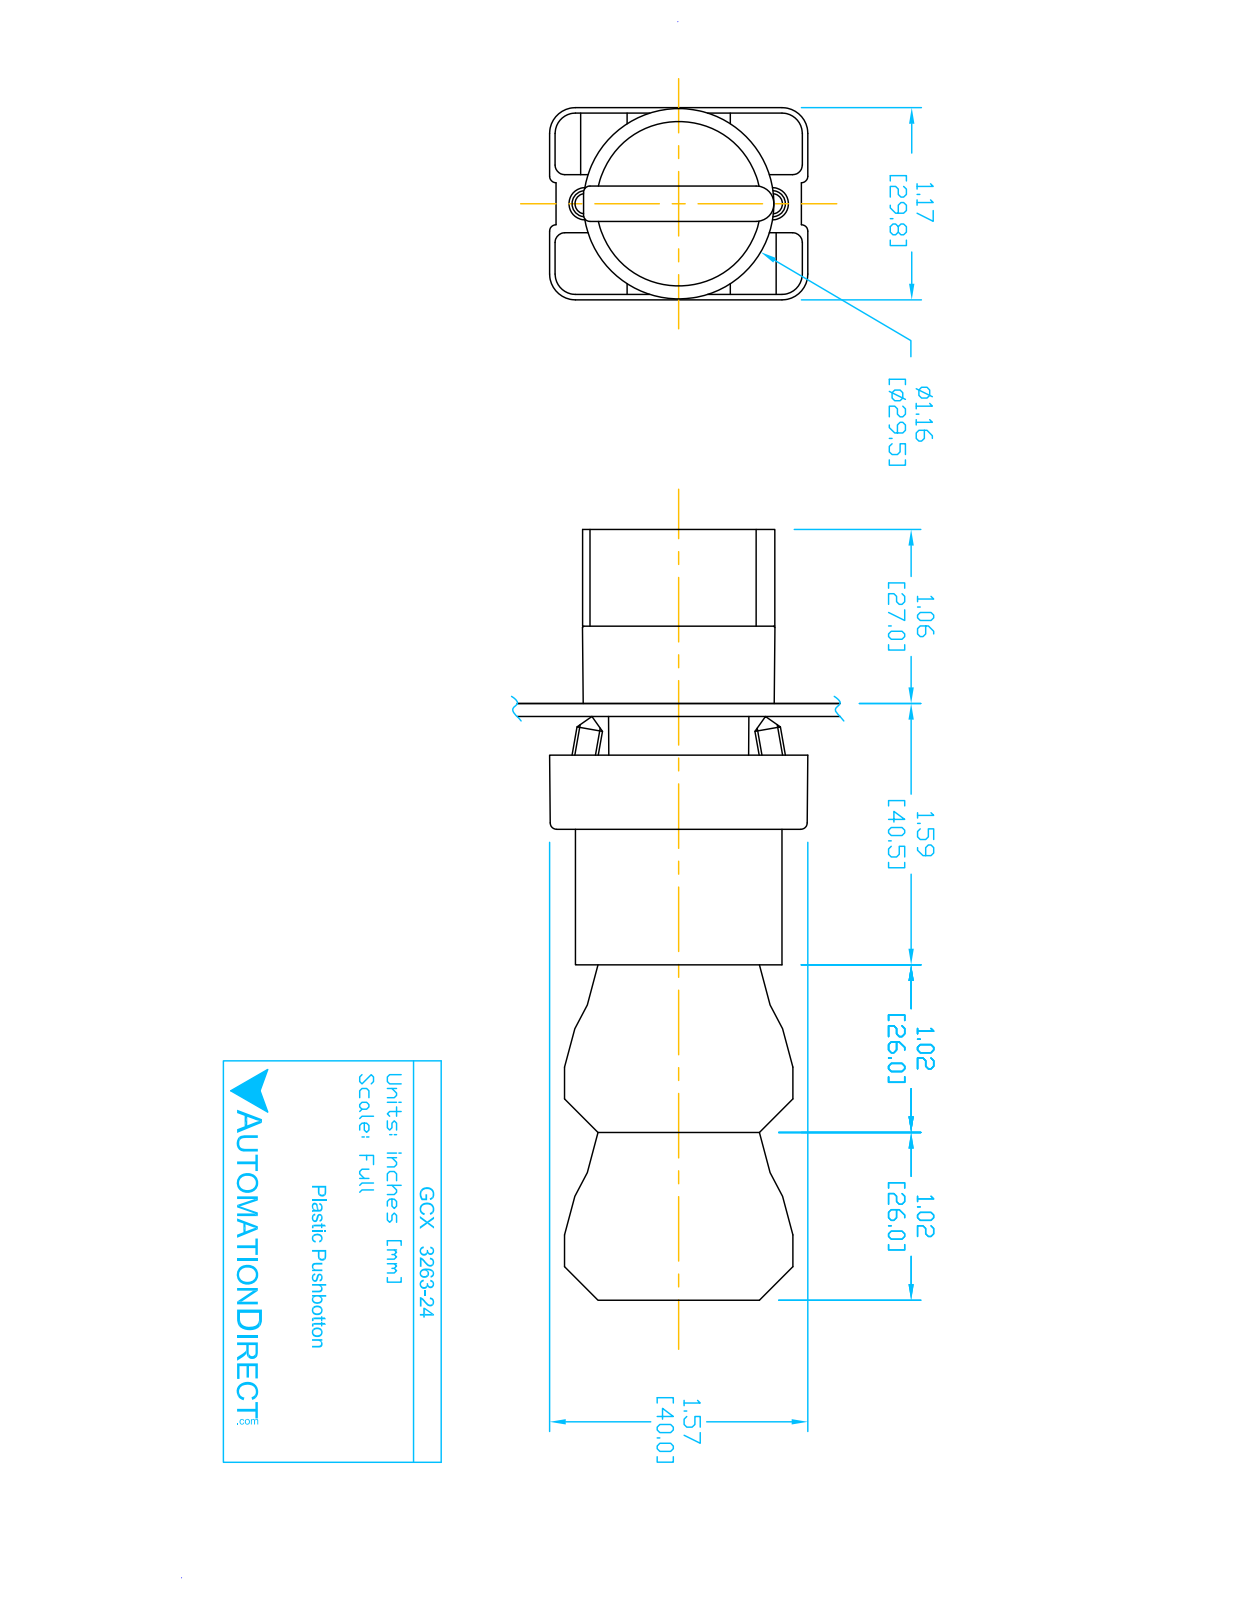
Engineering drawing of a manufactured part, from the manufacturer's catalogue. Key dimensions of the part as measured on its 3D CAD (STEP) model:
Part name (STEP PRODUCT): ECX1050; ECX3029-2; GCX3263-24; GCX3263 OPERATOR (+2 more)
STEP written by: SolidWorks 2016 (AUTOMOTIVE_DESIGN)
Units: inches
Bodies: 11 solids, 724 faces (488 planar, 193 cylindrical, 43 other)
Overall size (bounding box): 4.677 × 1.581 × 1.177
Volume: 4.751 in³ · Surface area: 59.22 in²
Round holes (diameter × count): ⌀0.079 ×4, ⌀0.087 ×2, ⌀0.124 ×2, ⌀0.13 ×2, ⌀0.197 ×1, ⌀0.469 ×1, ⌀0.878 ×1, ⌀0.888 ×1, ⌀1.024 ×1
Round bosses / shafts (diameter × count): ⌀0.157 ×4, ⌀1.175 ×1, ⌀1.004 ×1, ⌀0.945 ×1, ⌀0.856 ×1, ⌀0.78 ×1, ⌀0.504 ×1
Partial cylindrical surfaces — rounded edges, fillets, slot ends (radius × count): R0.059 ×24, R0.041 ×12, R0.124 ×12, R0.157 ×12, R0.039 ×9, R0.02 ×2, R0.063 ×2, R0.079 ×2
Main face-to-face distances: 0.579, 0.593, 1.024, 1.171, 0.014, 0.827, 1.85, 3.043, 2.02, 1.193
Hole centre spacings: 0.236, 1.003, 0.974, 0.472, 0.539, 0.544, 1.083, 0.484
